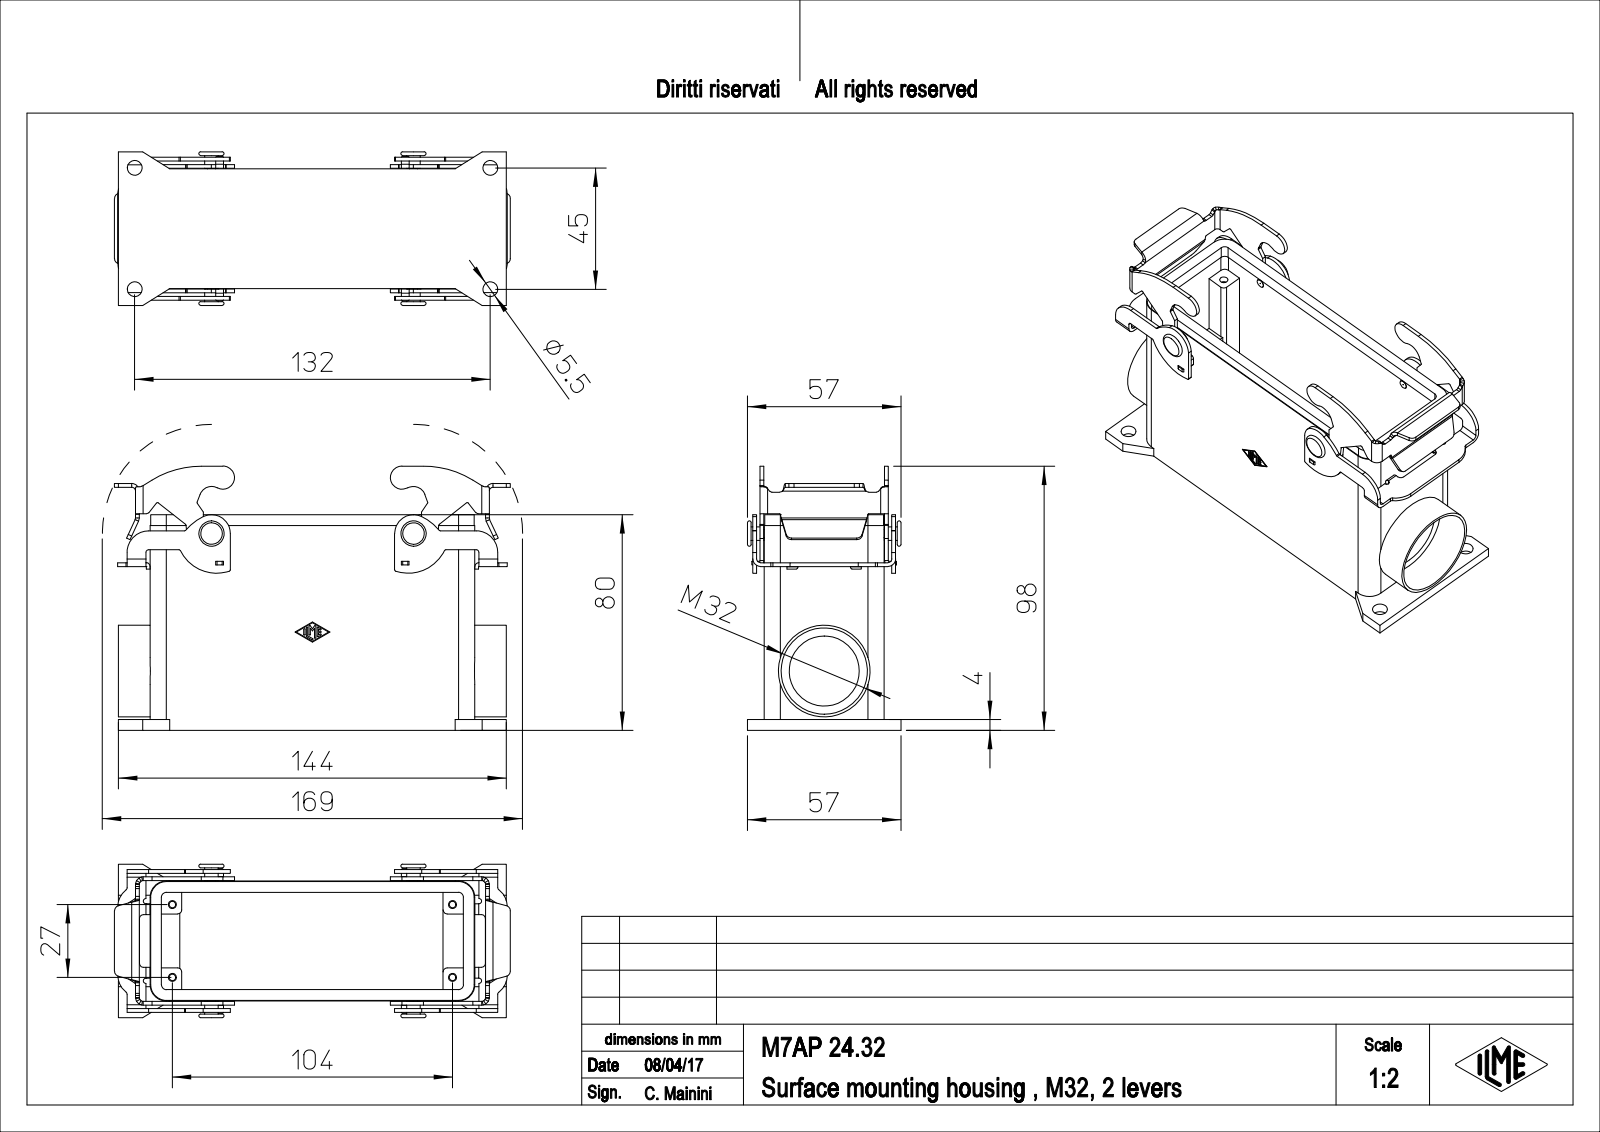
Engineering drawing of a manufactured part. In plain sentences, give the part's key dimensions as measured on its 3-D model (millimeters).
The part is named "M7AP_24.32". Its 3-D file was written by "PTC Creo Elements/Direct Modeling 19.0E 27-Jun-2016 (C) Parametric Technology GmbH (AUTOMOTIVE_DESIGN)". It is 1 solid with 609 faces: 295 planar, 270 cylindrical and 44 other. Overall it measures 146.97 by 98 by 57 millimeters. Its volume is 148 398 cubic millimeters and its surface area 84 088 square millimeters. Round holes: 4 of diameter 2.46, 4 of diameter 3, 4 of diameter 5.5, 2 of diameter 3.5, 1 of diameter 26, 1 of diameter 32. Round bosses or shafts: 2 of diameter 5, 2 of diameter 3.2, 2 of diameter 3, 1 of diameter 34. Partial cylindrical surfaces (rounded edges, fillets, slot ends): 22 of radius 0.5, 18 of radius 1, 16 of radius 0.25, 14 of radius 1.5, 12 of radius 2, 10 of radius 1.4, 10 of radius 2.8, 6 of radius 8. The main face-to-face distances are 4, 40.5, 44.5, 36.5, 1.4, 2.7, 48.9, 8.25, 11.75, 4.25. The hole center spacings are 16.64, 38.63, 118.34, 123.37, 27, 45, 104, 107.45.
